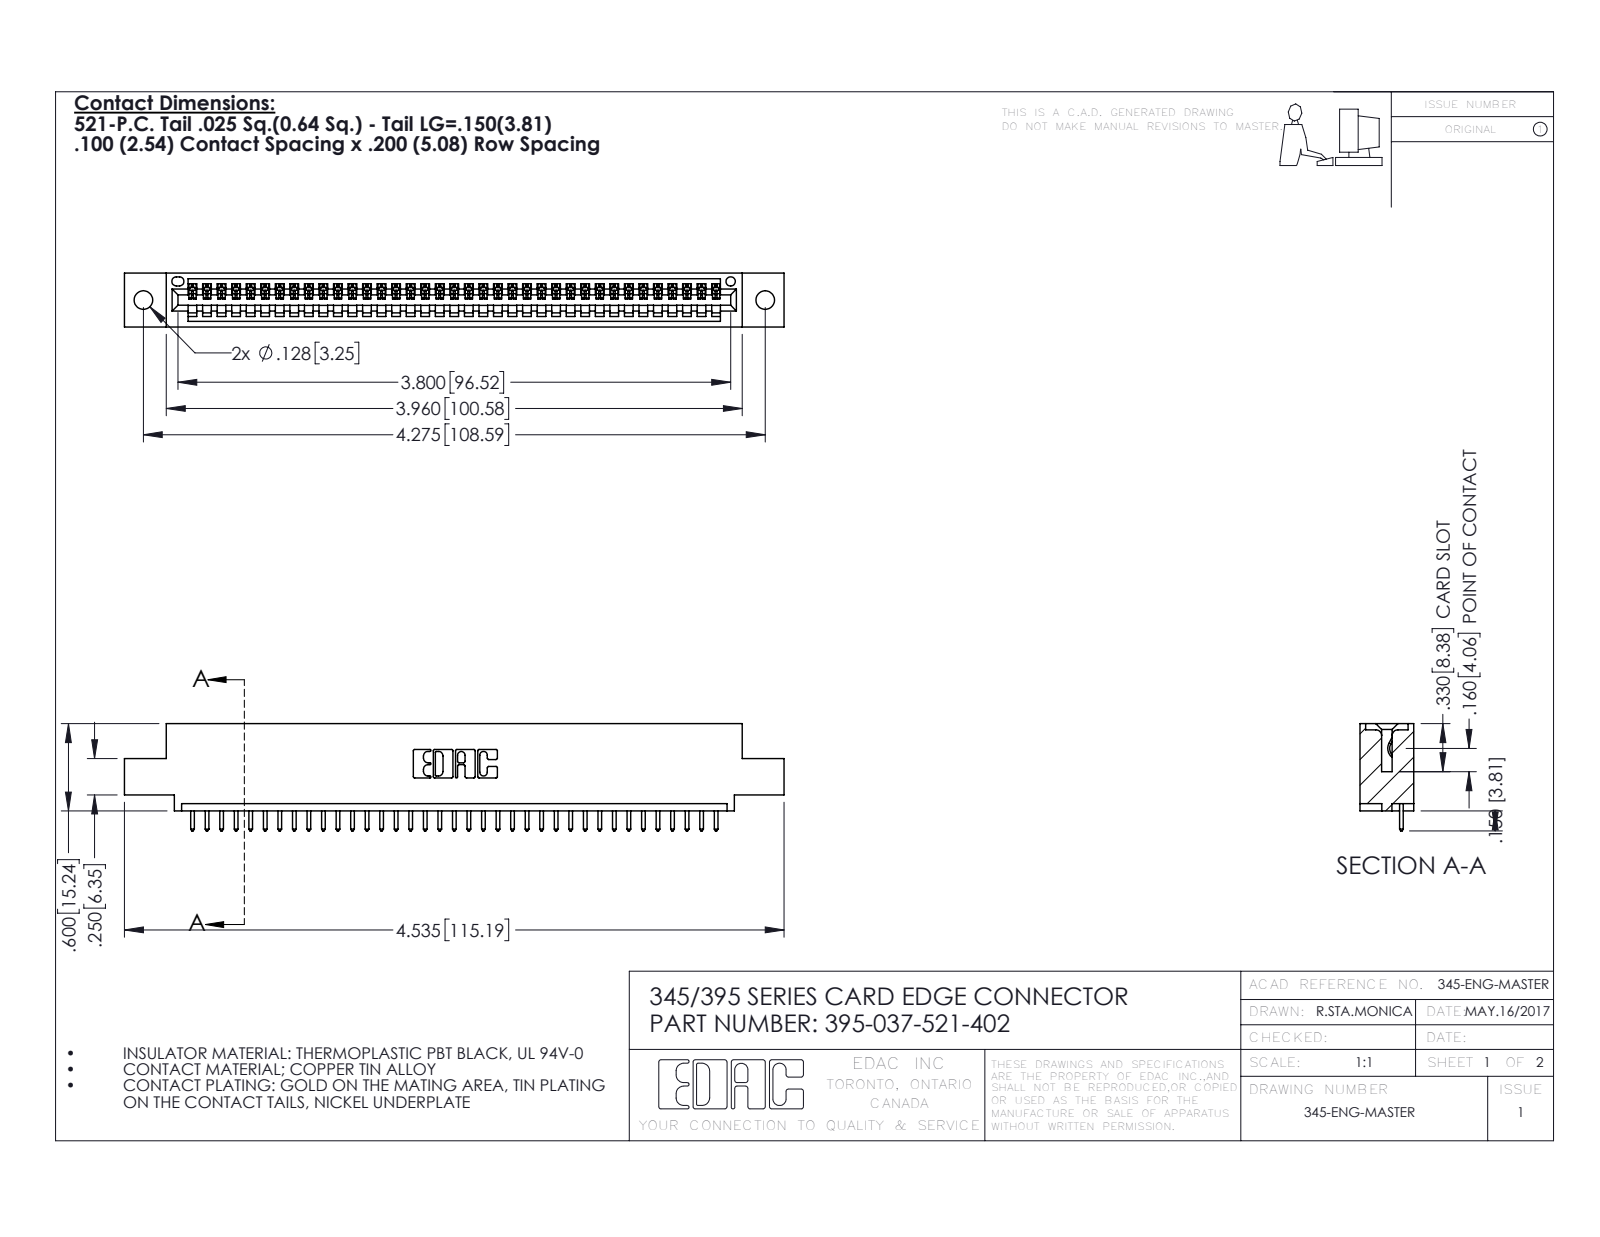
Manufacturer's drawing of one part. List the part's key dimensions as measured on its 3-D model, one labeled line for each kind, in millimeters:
Part name (STEP PRODUCT): 345 Part_0.110 Offset - 0.128 Dia; 345-292-001_345-293-121; 395-037-521-402
STEP written by: SolidWorks 2016 (CONFIG_CONTROL_DESIGN)
Units: millimetres
Bodies: 38 solids, 2276 faces (1564 planar, 712 cylindrical, 0 other)
Overall size (bounding box): 115.2 × 18.7 × 9.4
Volume: 10 700 mm³ · Surface area: 13 530 mm²
Round holes (diameter × count): ⌀3.3 ×2, ⌀1.6 ×1
Partial cylindrical surfaces — rounded edges, fillets, slot ends (radius × count): R0.2 ×74, R0.3 ×74, R0.3 ×22, R0.2 ×6, R0.8 ×6, R0.7 ×3, R0.8 ×2, R1 ×2
Main face-to-face distances: 1.8, 7.6, 9.4, 5.1, 2.5, 6.9, 0.6, 5.7, 3.8, 1.8
Hole centre spacings: 6.9, 102.6, 108.6
